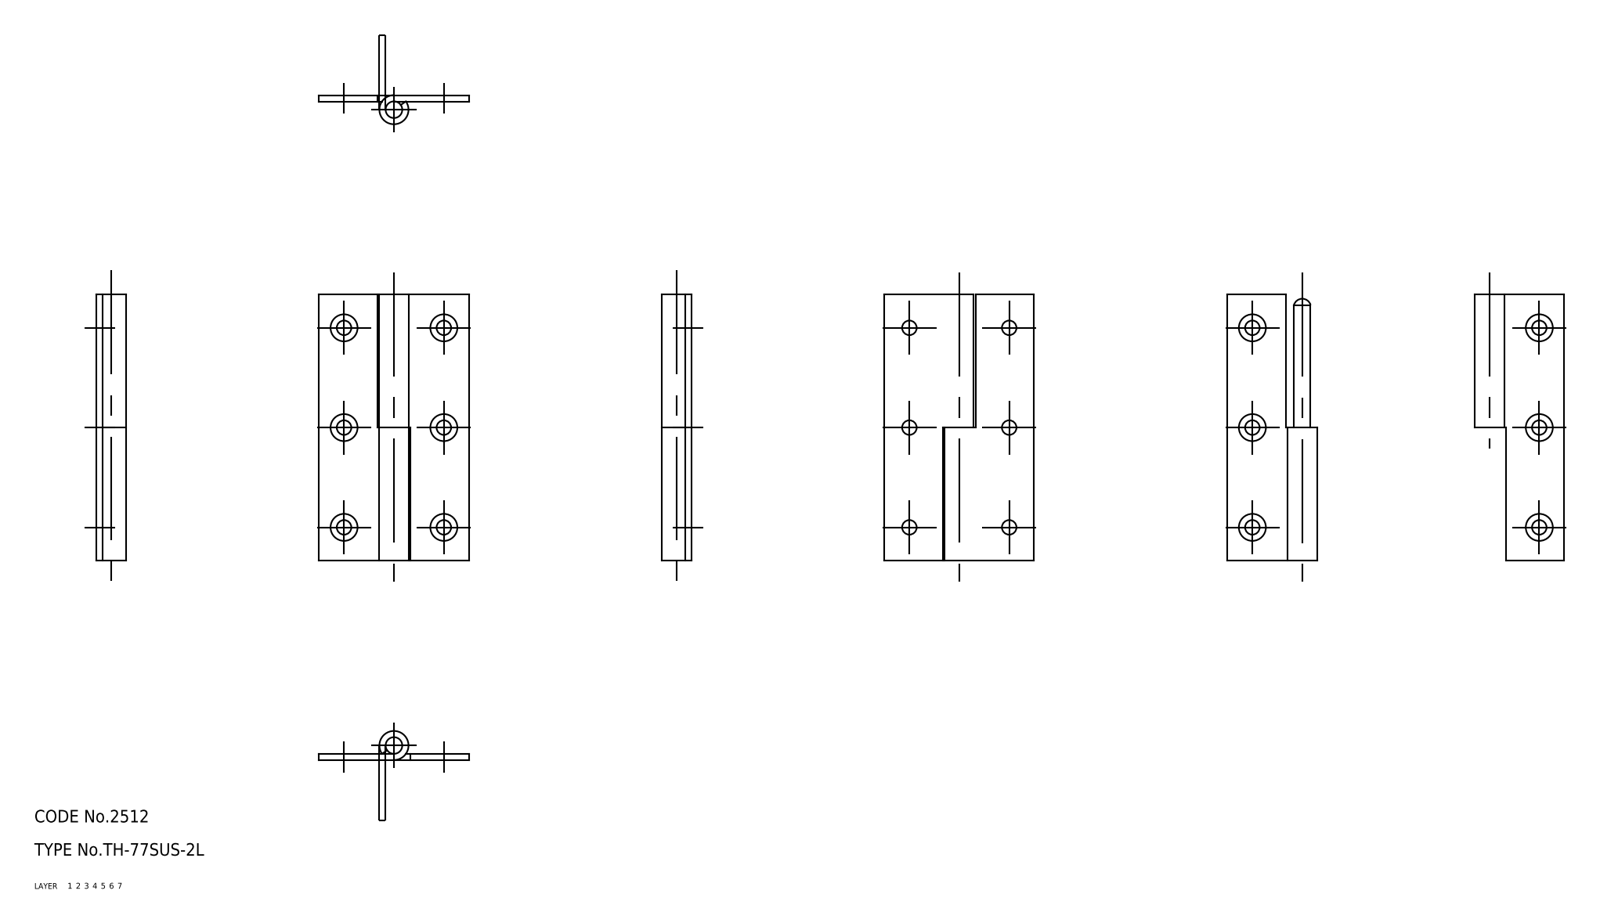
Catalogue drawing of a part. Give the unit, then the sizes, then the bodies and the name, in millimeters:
Units: millimetres
Overall size (bounding box): 64 × 36 × 7
Volume: 5 071 mm³ · Surface area: 7 285 mm²
Bodies: 3 solids, 36 faces (0 planar, 0 cylindrical, 36 other)
Part name (STEP PRODUCT): shaft; hinge piece_B; hinge piece_A; TH_77SUS_2L_16308_36
STEP written by: CADfix (AUTOMOTIVE_DESIGN)
